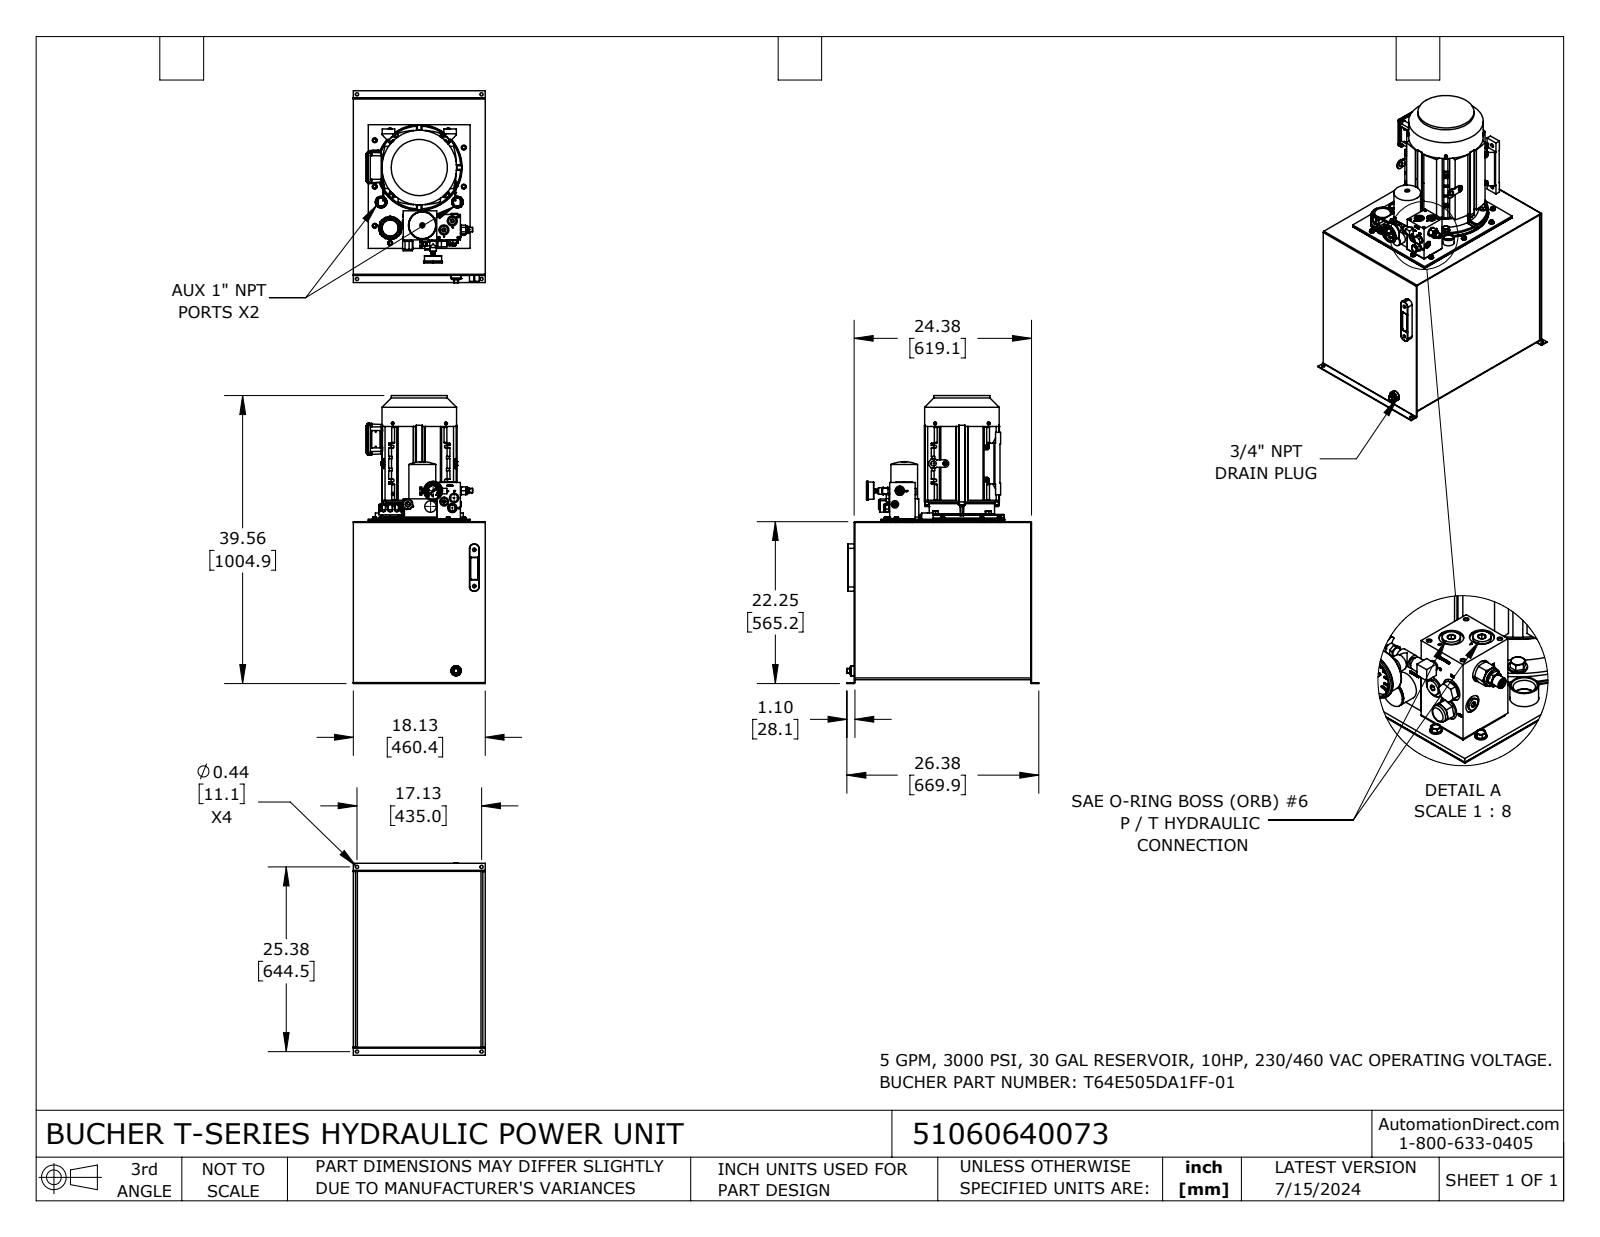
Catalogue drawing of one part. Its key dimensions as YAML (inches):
part_name: "51060640073"
step_written_by: "SolidWorks 2023 (CONFIG_CONTROL_DESIGN)"
units: inches
bodies: {solids: 134, faces: 6510, planar: 3305, cylindrical: 1786, other: 1419}
overall_size: [39.562, 26.4, 18.125]
volume: 1865
surface_area: 8039
round_holes:
  - {diameter: 0.437, count: 19}
  - {diameter: 0.5, count: 13}
  - {diameter: 0.236, count: 11}
  - {diameter: 0.197, count: 10}
  - {diameter: 0.563, count: 10}
  - {diameter: 0.315, count: 9}
  - {diameter: 0.201, count: 8}
  - {diameter: 0.268, count: 8}
  - {diameter: 0.19, count: 6}
  - {diameter: 0.422, count: 6}
  - {diameter: 0.531, count: 6}
  - {diameter: 0.12, count: 5}
round_bosses_or_shafts:
  - {diameter: 0.313, count: 11}
  - {diameter: 0.676, count: 10}
  - {diameter: 0.551, count: 9}
  - {diameter: 0.472, count: 9}
  - {diameter: 0.315, count: 7}
  - {diameter: 0.197, count: 7}
  - {diameter: 0.373, count: 6}
  - {diameter: 0.25, count: 5}
partial_cylinders:
  - {radius: 0.02, count: 148}
  - {radius: 0.079, count: 68}
  - {radius: 0.039, count: 52}
  - {radius: 0.118, count: 52}
  - {radius: 0.05, count: 37}
  - {radius: 0.25, count: 36}
  - {radius: 0.063, count: 20}
  - {radius: 0.375, count: 15}
face_to_face_distances: [0.104, 24.27, 21.635, 0.105, 17.5, 17.395, 17.291, 17.396, 24.375, 24.166]
hole_center_spacings: [3.469, 4.646, 4.764, 3.799, 6.232, 9.489, 9.137, 9.137]
